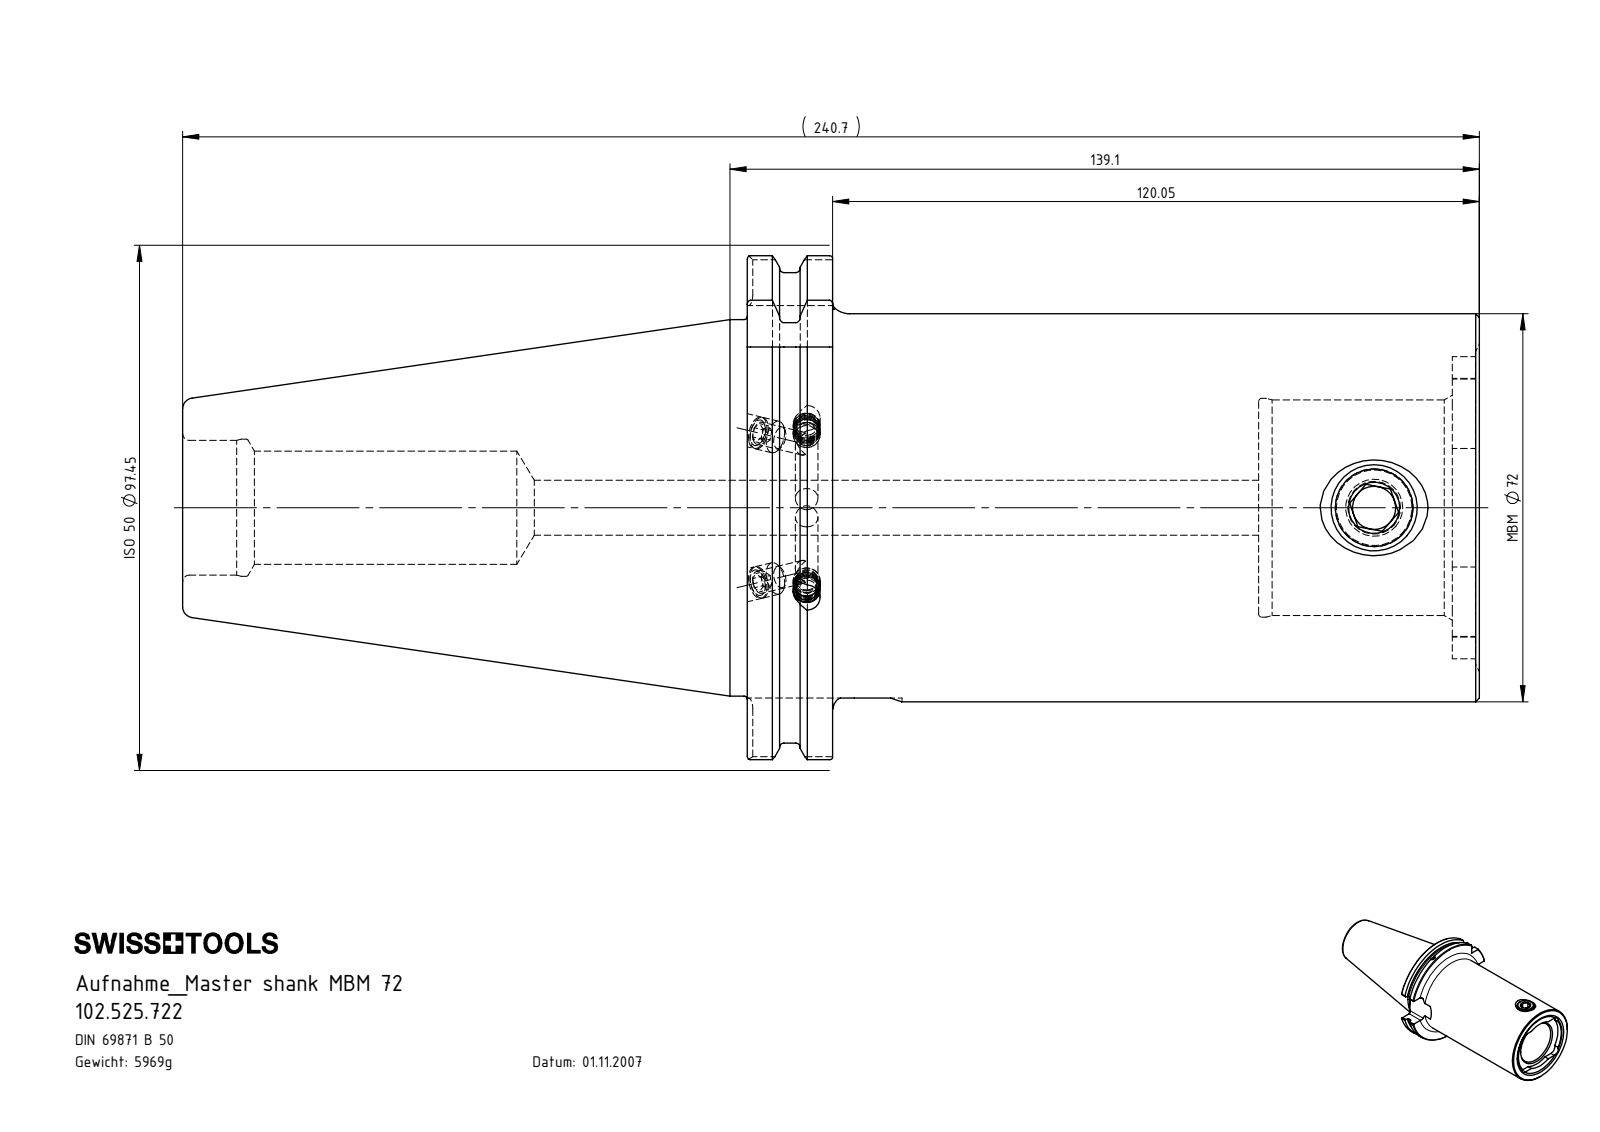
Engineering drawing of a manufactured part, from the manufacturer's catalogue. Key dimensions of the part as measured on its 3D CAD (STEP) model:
Part name (STEP PRODUCT): SB5-MB7.K01.139_D_mit Bundkhlung; 102.525.722; KVT_MB_600_050; MB7-ER1.001.022_A (+1 more)
STEP written by: SolidWorks 2017 (CONFIG_CONTROL_DESIGN)
Units: millimetres
Bodies: 8 solids, 302 faces (80 planar, 83 cylindrical, 139 other)
Overall size (bounding box): 240.7 × 97.45 × 93.51
Volume: 760 540 mm³ · Surface area: 79 830 mm²
Round holes (diameter × count): ⌀4.2 ×3, ⌀4 ×2, ⌀6 ×2, ⌀5 ×1, ⌀8 ×1, ⌀10.2 ×1, ⌀14.5 ×1, ⌀21 ×1, ⌀25 ×1, ⌀25.45 ×1, ⌀40 ×1, ⌀40.6 ×1
Round bosses / shafts (diameter × count): ⌀91 ×1, ⌀72 ×1, ⌀69.85 ×1, ⌀16 ×1, ⌀5 ×1
Partial cylindrical surfaces — rounded edges, fillets, slot ends (radius × count): R2 ×8, R5.2 ×4, R12.85 ×1, R23.75 ×1, R28.02 ×1, R48.73 ×1
Main face-to-face distances: 15.85, 94.9, 79.05, 135.9, 120.05, 41, 130.85, 115, 35.95, 5.05
